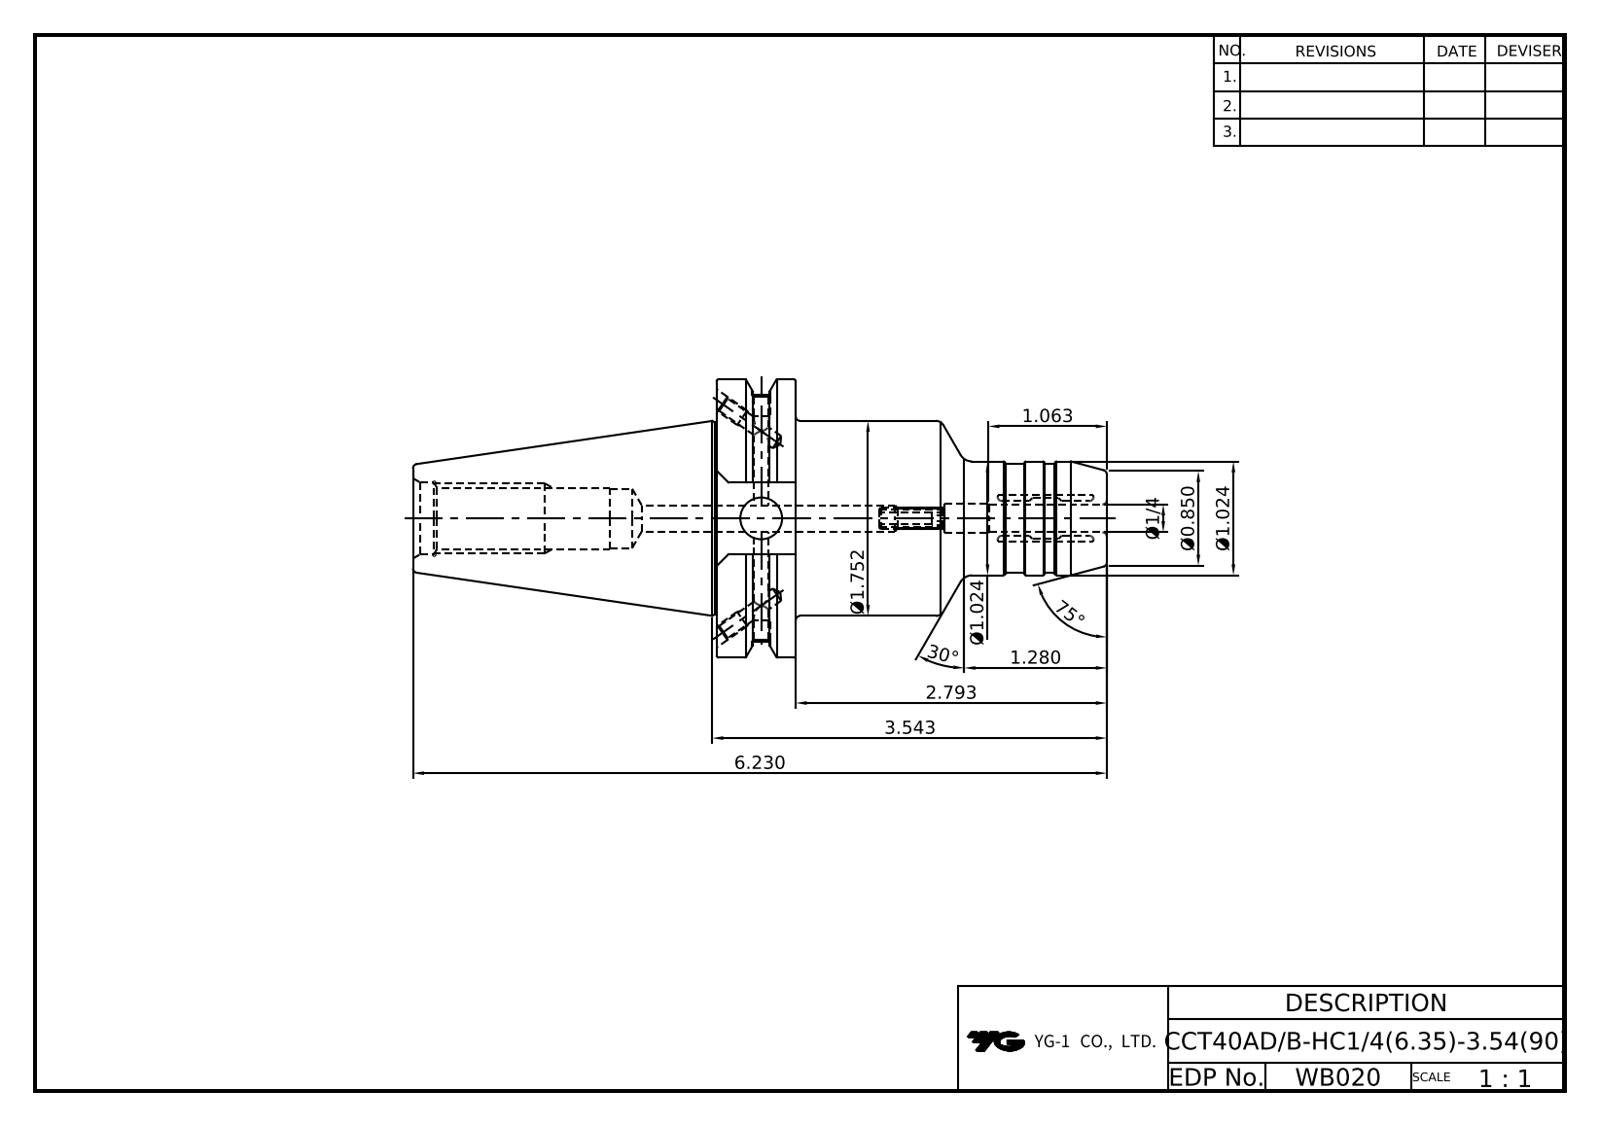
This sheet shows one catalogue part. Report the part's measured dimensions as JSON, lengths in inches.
{"part_name": "LO-CCT40ADB-HC6.35-90", "step_written_by": "Autodesk Inventor 2022 (AUTOMOTIVE_DESIGN)", "units": "inches", "bodies": {"solids": 1, "faces": 112, "planar": 34, "cylindrical": 35, "other": 43}, "overall_size": [6.23, 2.5, 2.405], "volume_in3": 10.9, "surface_area_in2": 44.74, "round_holes": [[0.128, 4], [0.157, 2], [0.165, 2], [0.169, 1], [0.236, 1], [0.25, 1], [0.268, 1], [0.375, 1], [0.512, 1], [0.527, 1], [0.642, 1]], "round_bosses_or_shafts": [[2.5, 1], [1.752, 1], [1.724, 1], [1.024, 1], [0.984, 1]], "partial_cylinders_radius": [[1.108, 1]], "face_to_face_distances": [0.711, 3.504, 2.793, 1.874, 0.645, 2.726, 3.437, 6.23, 3.202, 0.476]}
